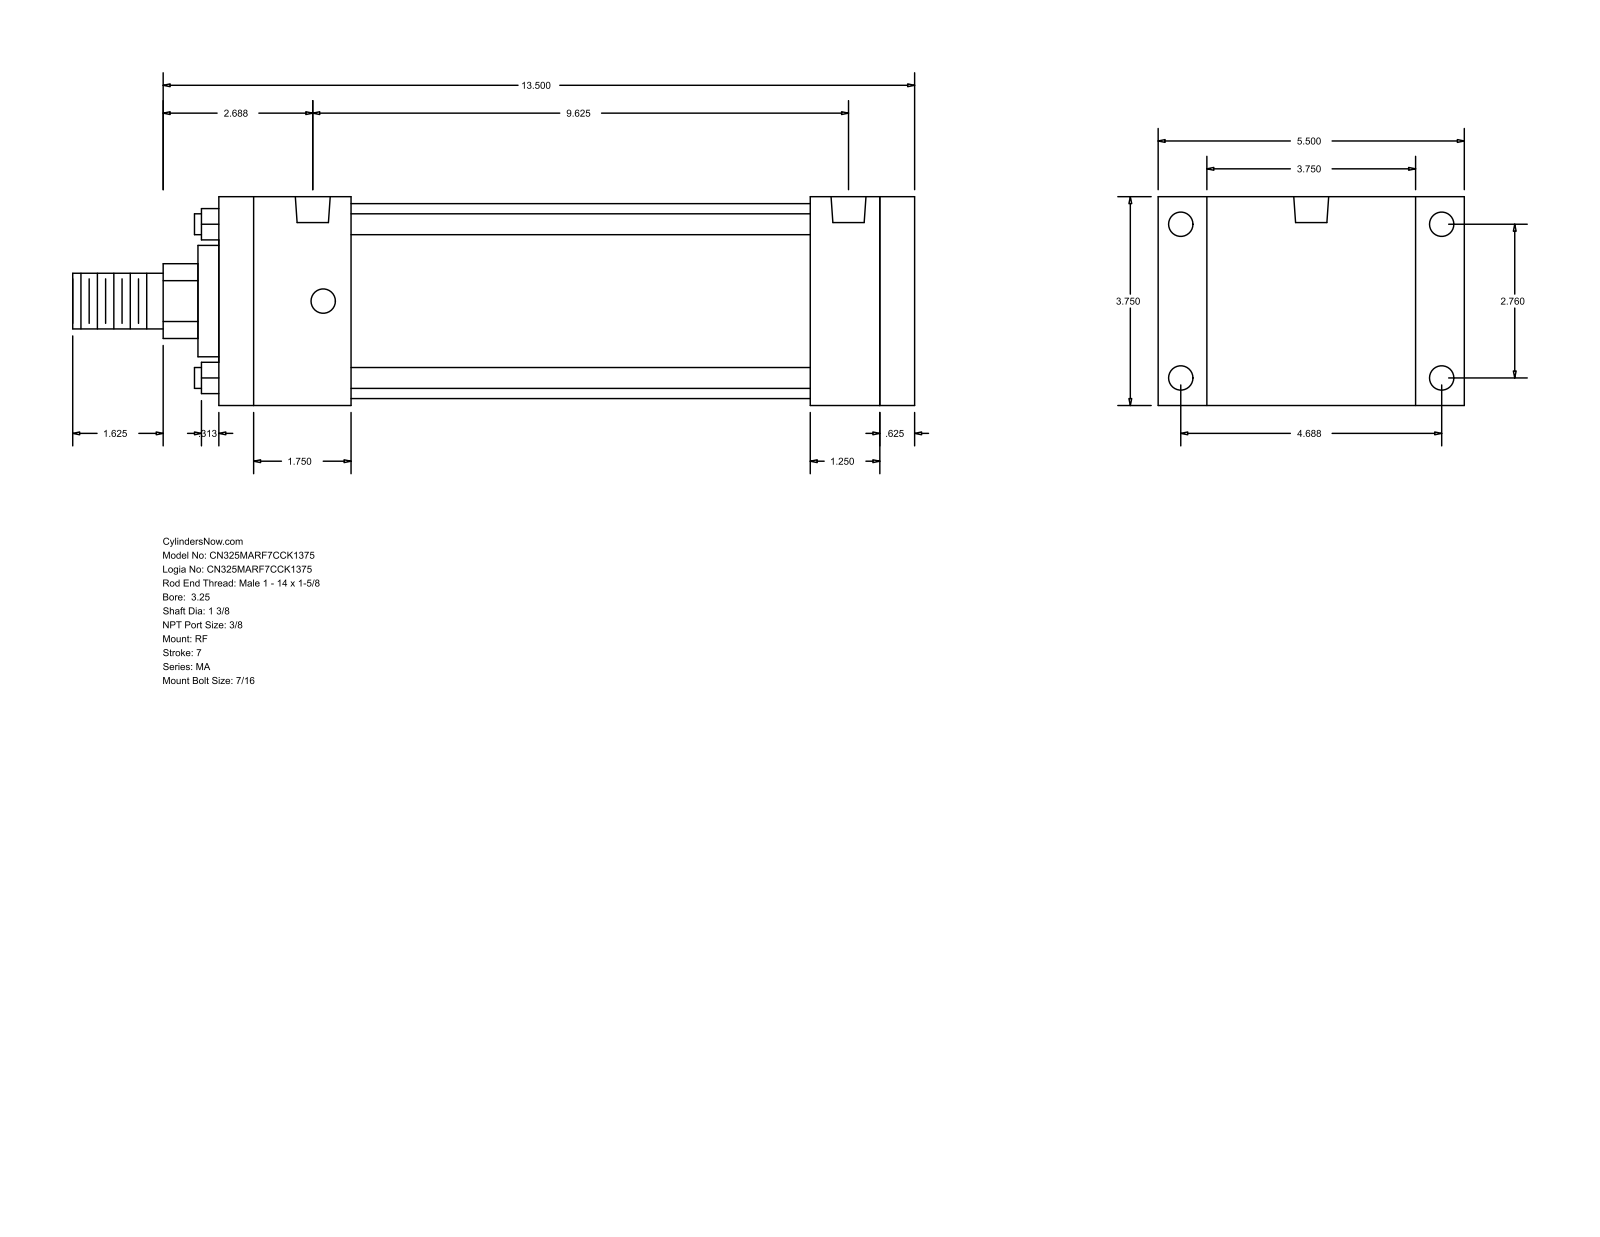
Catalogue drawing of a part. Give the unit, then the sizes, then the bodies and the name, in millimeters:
Units: millimetres
Overall size (bounding box): 384.18 × 139.7 × 95.25
Round holes (diameter × count): ⌀11.11 ×8, ⌀15.93 ×2
Round bosses / shafts (diameter × count): ⌀9.53 ×4, ⌀88.9 ×1, ⌀50.8 ×1, ⌀34.92 ×1, ⌀25.4 ×1
Partial cylindrical surfaces — rounded edges, fillets, slot ends (radius × count): R17.06 ×1
Main face-to-face distances: 95.24, 317.5, 15.88, 301.62, 22.23, 117.47, 269.87, 31.75, 47.63, 60.32
Hole centre spacings: 70.1, 119.06, 138.16, 234.95, 4.76, 4.77, 239.71, 239.72
Bodies: 0 solids, 92 faces (64 planar, 28 cylindrical, 0 other)
Part name (STEP PRODUCT): MA_RF__0325_1.375
STEP written by: GSSL Pune (CONFIG_CONTROL_DESIGN)
